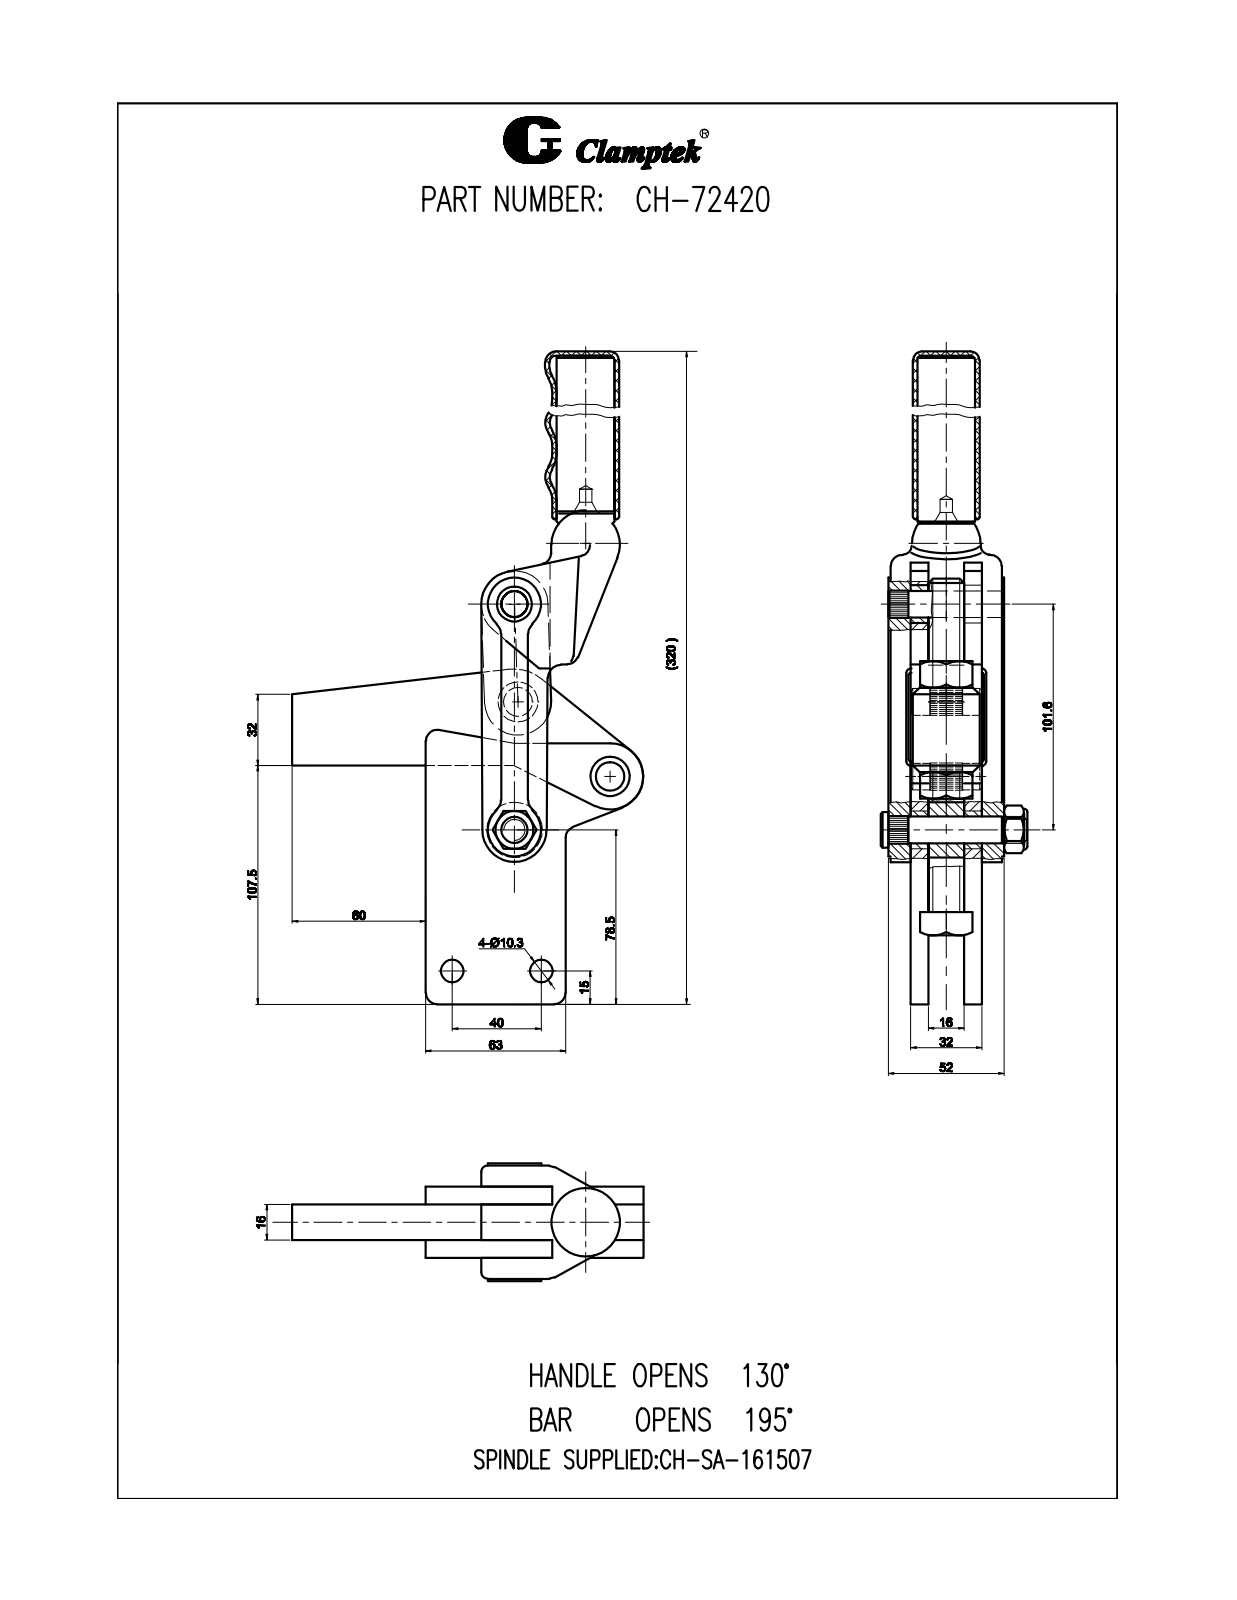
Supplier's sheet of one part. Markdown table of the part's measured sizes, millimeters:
| quantity | value |
| --- | --- |
| part name | CH-72420; 72425-11; CH-72420-01; CH-72420-02 (+8 more) |
| STEP written by | SolidWorks 2011 (CONFIG_CONTROL_DESIGN) |
| units | millimeters |
| bodies | 41 solids, 4514 faces (2704 planar, 1520 cylindrical, 290 other) |
| overall size | 9258.79 × 607.8 × 68.5 |
| volume | 467 739 mm³ |
| surface area | 164 219 mm² |
| round holes (diameter × count) | 10.5 × 1, 13.2 × 1, 18 × 1, 21.25 × 1, 24.6 × 1 |
| round bosses / shafts (diameter × count) | 13 × 4, 12.5 × 4, 18 × 3, 29.8 × 1, 26.75 × 1, 25 × 1, 16 × 1, 13.8 × 1 |
| partial cylindrical surfaces (radius × count) | 0.5 × 8, 1 × 6, 7 × 6, 5 × 5, 8.7 × 3, 15 × 3, 6 × 2, 8.5 × 2 |
| main face-to-face distances | 24, 8, 16, 32, 9.15, 23.85, 1, 41.85, 40.85, 8.15 |
